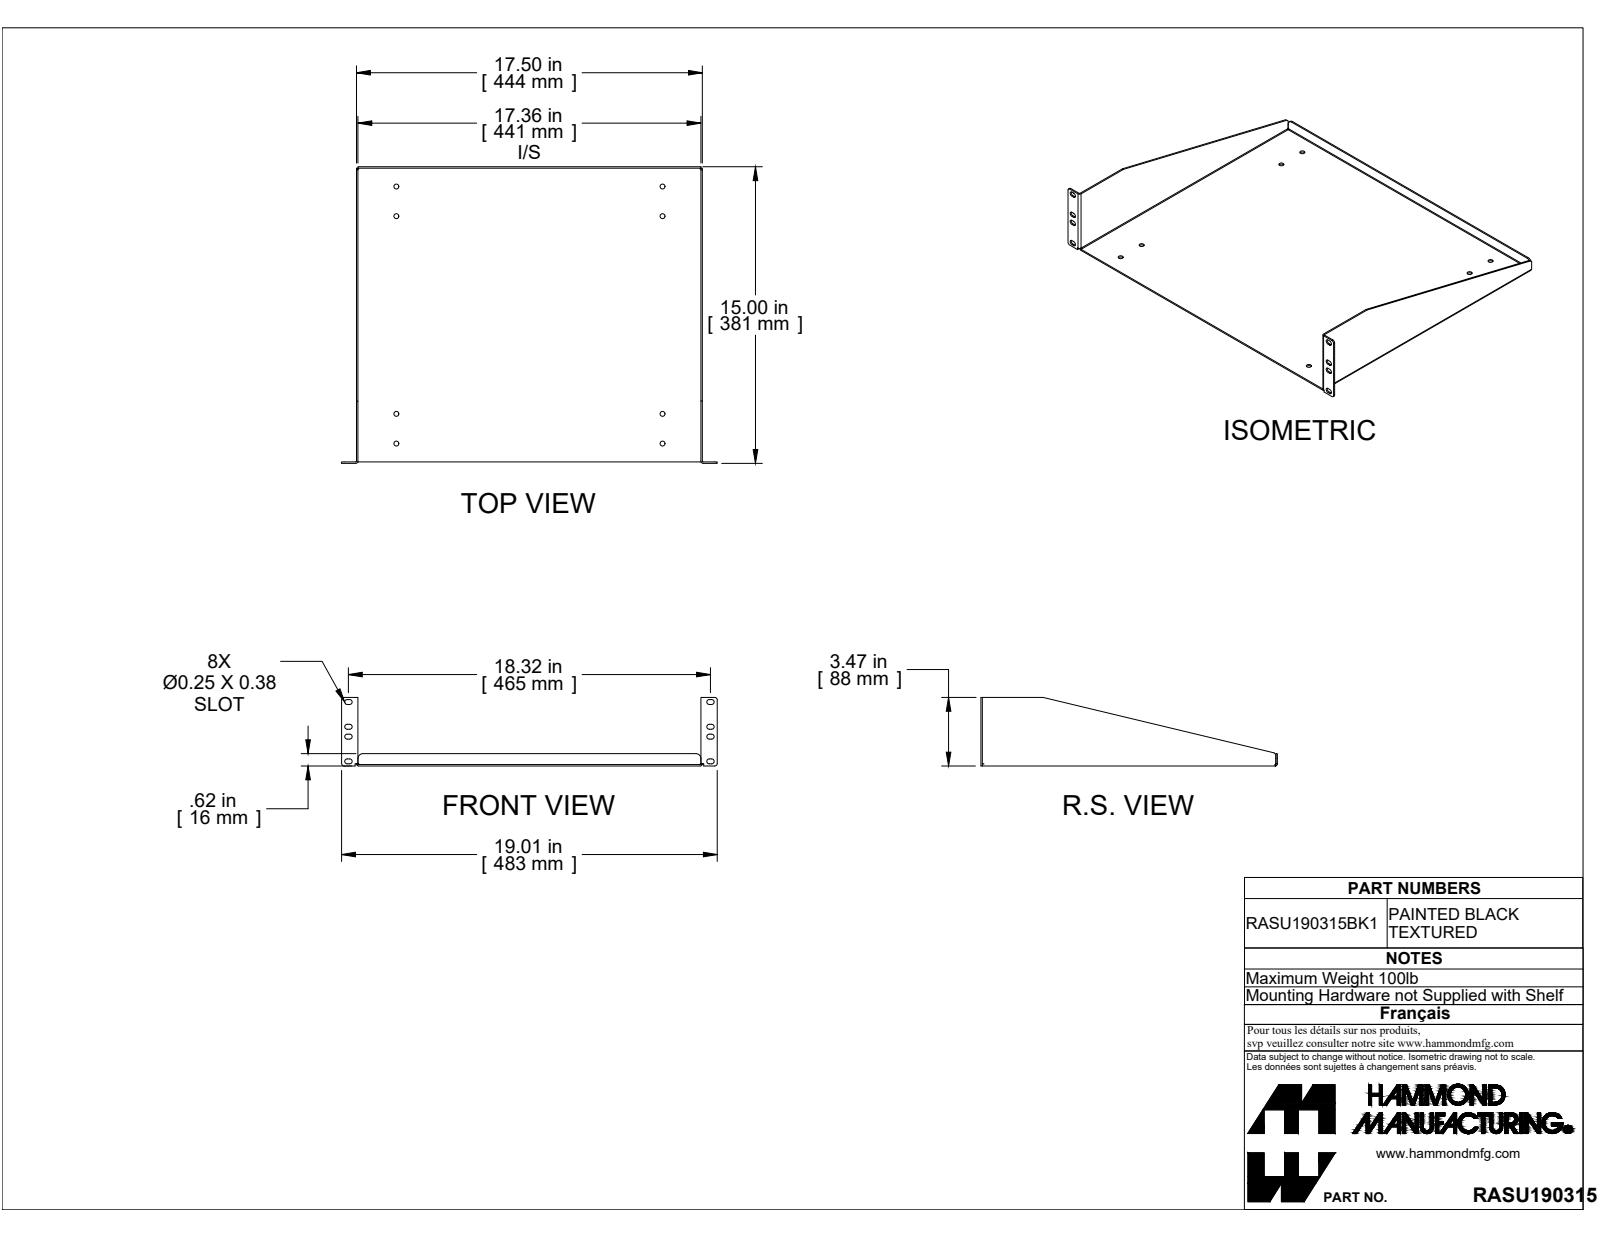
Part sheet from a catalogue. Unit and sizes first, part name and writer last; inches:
Units: inches
Overall size (bounding box): 19.006 × 15 × 3.468
Round holes (diameter × count): ⌀0.25 ×8
Partial cylindrical surfaces — rounded edges, fillets, slot ends (radius × count): R0.125 ×20, R0.036 ×5, R0.108 ×5, R0.055 ×3, R0.25 ×2
Main face-to-face distances: 0.072, 17.428, 17.356, 17.5, 14.856, 14.928, 0.072, 14.928, 15, 0.625
Hole centre spacings: 1.5, 11.5, 13.468, 13.551, 17.709, 10, 13, 16.774
Volume: 24.58 in³ · Surface area: 689.4 in²
Bodies: 1 solid, 104 faces (56 planar, 44 cylindrical, 4 other)
Part name (STEP PRODUCT): RASU190315BK1
STEP written by: SolidWorks 2019 (CONFIG_CONTROL_DESIGN)
